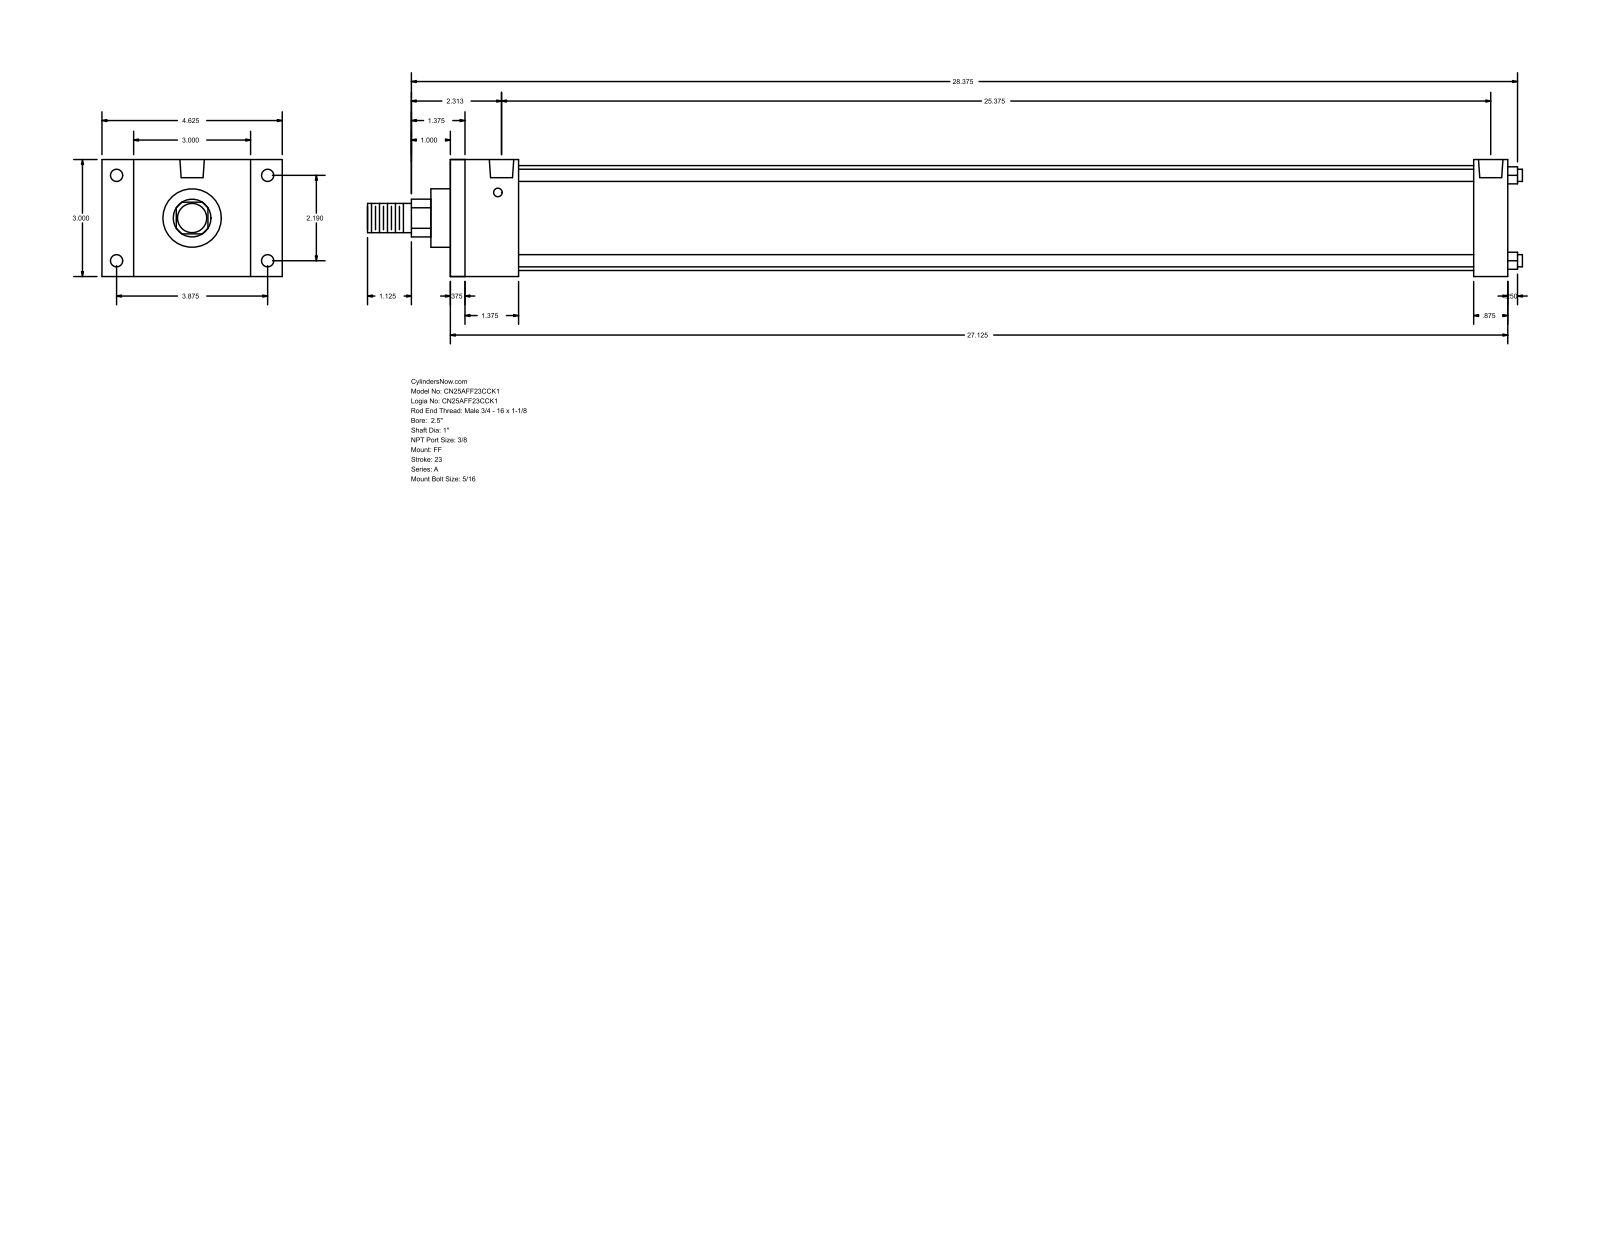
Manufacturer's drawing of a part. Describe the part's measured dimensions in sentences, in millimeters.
The part is named "A_FF__0250_1". Its 3-D file was written by "GSSL Pune (CONFIG_CONTROL_DESIGN)". It is 0 solids with 92 faces: 64 planar, 28 cylindrical and 0 other. Overall it measures 752.48 by 117.47 by 76.2 millimeters. Round holes: 4 of diameter 5.56, 4 of diameter 7.94, 2 of diameter 15.93. Round bosses or shafts: 4 of diameter 7.94, 1 of diameter 68.33, 1 of diameter 38.1, 1 of diameter 25.4, 1 of diameter 19.05. Partial cylindrical surfaces (rounded edges, fillets, slot ends): 1 of radius 12.29. The main face-to-face distances are 76.2, 688.98, 9.52, 679.46, 44.45, 666.75, 34.93, 657.23, 622.3, 644.53. The hole center spacings are 2.38, 55.62, 98.42, 113.05, 646.9, 649.28, 644.52.
